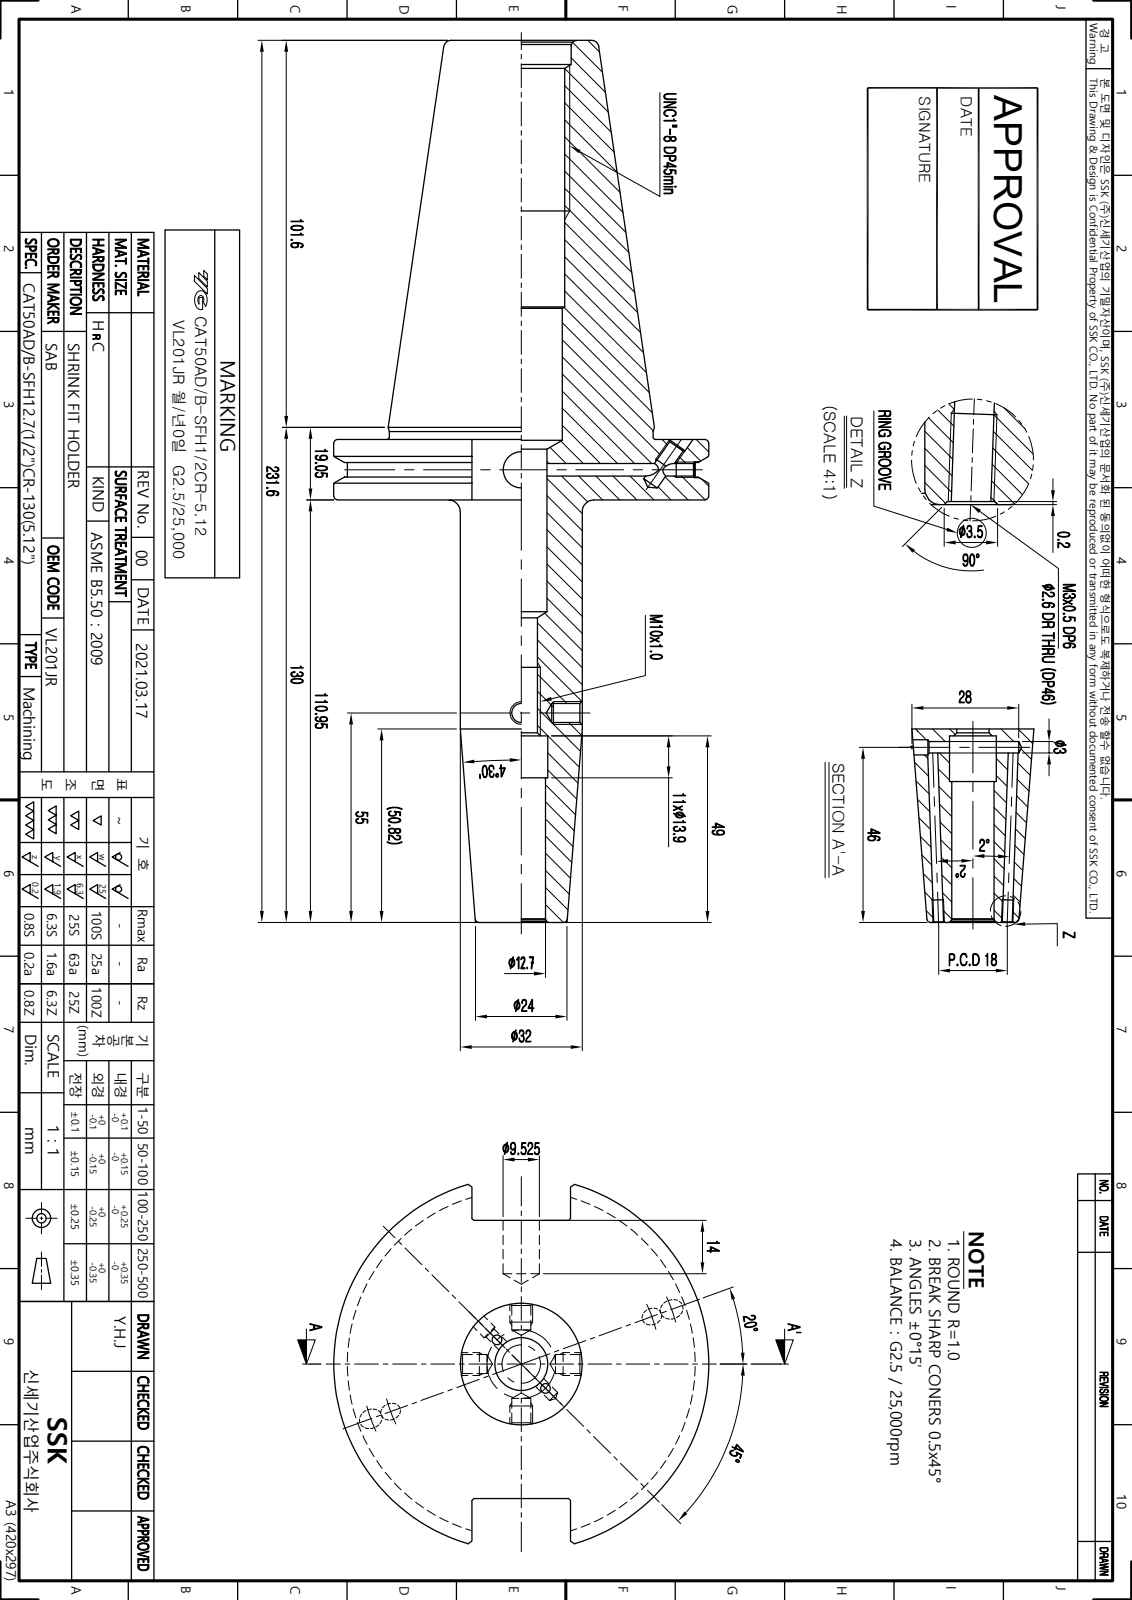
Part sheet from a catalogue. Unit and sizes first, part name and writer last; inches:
Units: inches
Overall size (bounding box): 9.118 × 3.875 × 3.728
Round holes (diameter × count): ⌀0.097 ×2, ⌀0.128 ×2, ⌀0.163 ×2, ⌀0.165 ×2, ⌀0.197 ×2, ⌀0.118 ×1, ⌀0.157 ×1, ⌀0.351 ×1, ⌀0.375 ×1, ⌀0.5 ×1, ⌀0.531 ×1, ⌀0.547 ×1
Round bosses / shafts (diameter × count): ⌀3.875 ×1, ⌀3.594 ×1, ⌀2.726 ×1, ⌀1.26 ×1
Main face-to-face distances: 0.625, 4.125, 4.75, 2.875, 1.02, 9.118, 4.993, 4.368, 4.363, 0.238
Volume: 23.71 in³ · Surface area: 92.76 in²
Bodies: 1 solid, 95 faces (37 planar, 33 cylindrical, 25 other)
Part name (STEP PRODUCT): LO-CAT50ADB-SFH12.7CR-130
STEP written by: Autodesk Inventor 2022 (AUTOMOTIVE_DESIGN)
